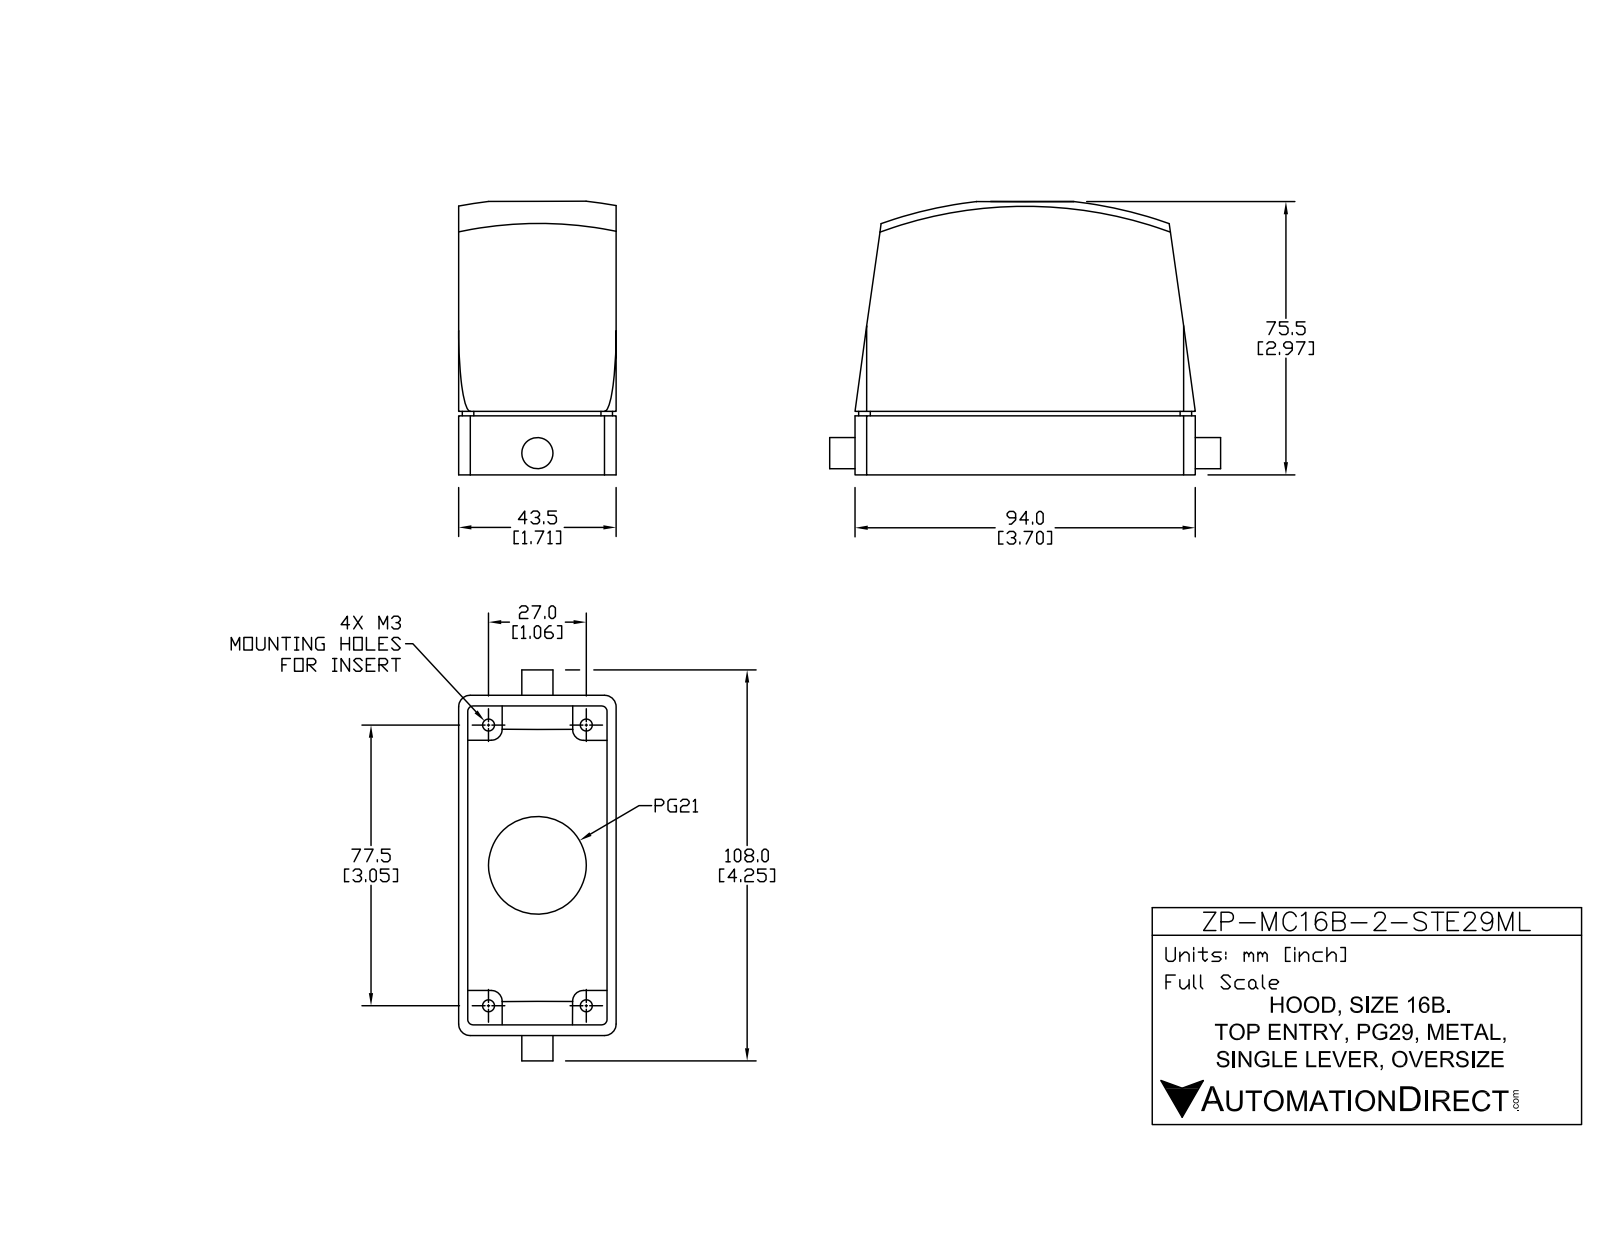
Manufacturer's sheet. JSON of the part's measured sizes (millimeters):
{"part_name": "ZP-MC16B-2-STE29ML", "step_written_by": "SolidWorks 2011 (AUTOMOTIVE_DESIGN)", "units": "millimeters", "bodies": {"solids": 5, "faces": 86, "planar": 52, "cylindrical": 28, "other": 6}, "overall_size": [108, 76.31, 43.5], "volume_mm3": 66750, "surface_area_mm2": 50880, "round_holes": [[3.5, 4], [35, 1]], "round_bosses_or_shafts": [[8.6, 1]], "partial_cylinders_radius": [[3.2, 8], [1.5, 4], [3, 4], [0.7, 1]], "face_to_face_distances": [2.5, 41, 43.5, 38.5, 9.5, 78.58, 2.96, 91.04, 81.54, 12.46], "hole_center_spacings": [42.31, 28.96, 79.5, 84.61]}
